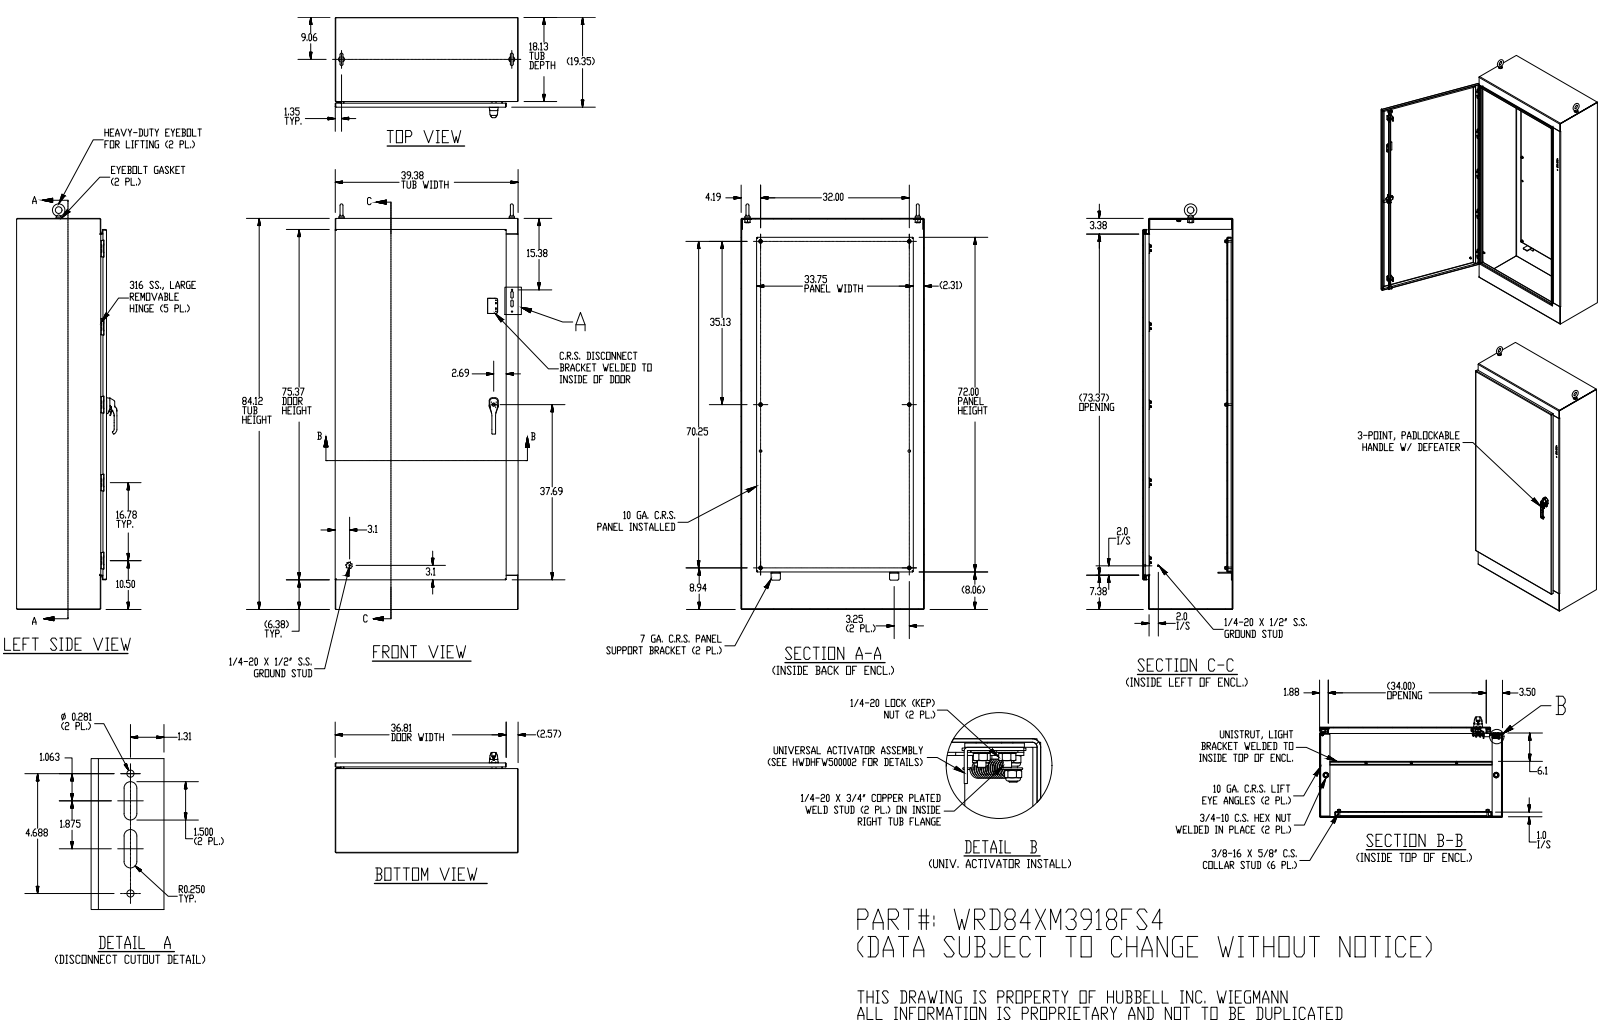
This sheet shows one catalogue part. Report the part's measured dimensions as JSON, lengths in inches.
{"part_name": "WRD84XM3918FS4", "step_written_by": "SolidWorks 2019 (AUTOMOTIVE_DESIGN)", "units": "inches", "bodies": {"solids": 144, "faces": 4198, "planar": 1739, "cylindrical": 1409, "other": 1050}, "overall_size": [87.248, 39.379, 21.598], "volume_in3": 1692, "surface_area_in2": 30415, "round_holes": [[0.195, 10], [0.266, 10], [0.294, 10], [0.65, 10], [0.25, 9], [0.277, 8], [0.563, 8], [0.156, 6], [0.307, 6], [0.2, 4], [0.29, 4], [0.196, 3]], "round_bosses_or_shafts": [[0.625, 19], [0.25, 10], [0.33, 8], [0.563, 6], [0.533, 4], [0.337, 4], [0.375, 3], [0.236, 3]], "partial_cylinders_radius": [[0.02, 187], [0.012, 109], [0.02, 52], [0.062, 25], [0.019, 21], [0.094, 19], [0.05, 18], [0.063, 18]], "face_to_face_distances": [0.104, 19.245, 39.271, 19.141, 19.349, 0.134, 1, 1.238, 1.134, 18.007], "hole_center_spacings": [1, 32, 16.781, 16.781, 33.563, 50.344, 33.465, 35.125]}
